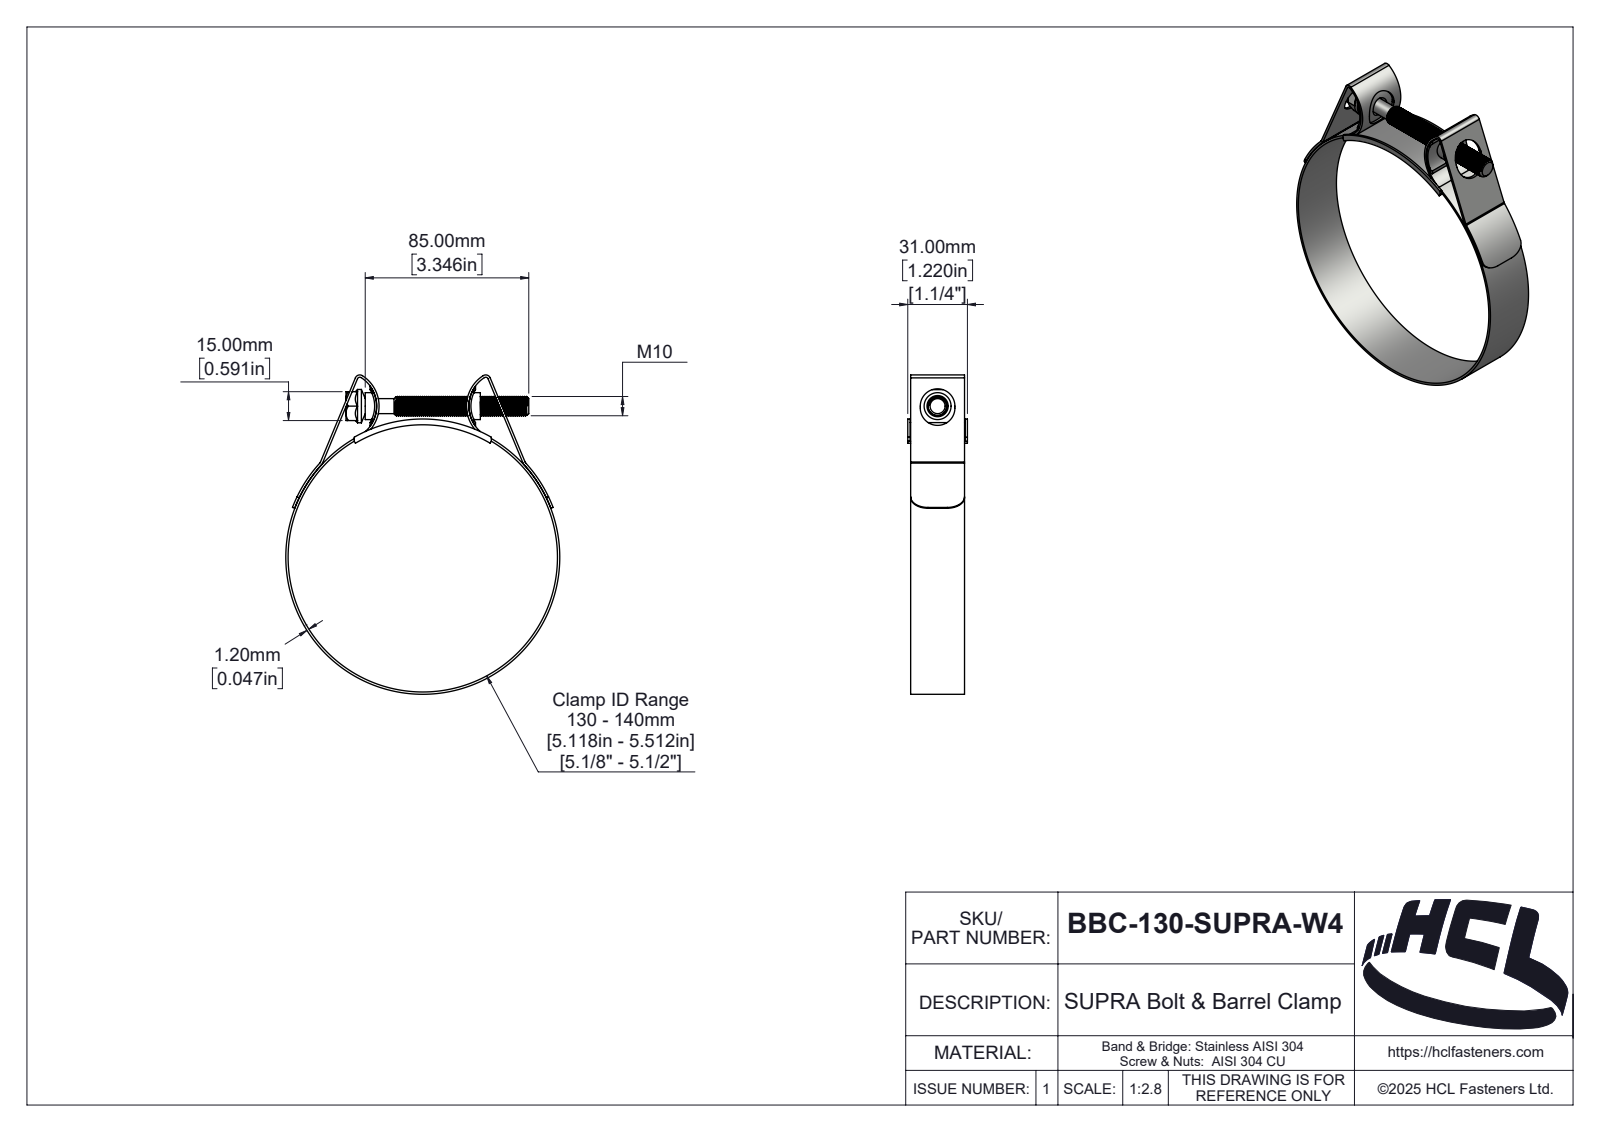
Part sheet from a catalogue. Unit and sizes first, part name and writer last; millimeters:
Units: millimetres
Overall size (bounding box): 165.9 × 142.4 × 31
Round holes (diameter × count): ⌀140 ×1
Round bosses / shafts (diameter × count): ⌀142.4 ×1, ⌀17.32 ×1, ⌀14 ×1, ⌀10 ×1, ⌀7.8 ×1
Partial cylindrical surfaces — rounded edges, fillets, slot ends (radius × count): R1 ×4, R1.3 ×2, R2 ×2, R2.5 ×2, R3.2 ×2, R9 ×2, R16.49 ×2, R17.49 ×2
Main face-to-face distances: 1.2, 28, 1.5, 29.5, 29.8, 28.3, 31, 28.6, 15, 2.5
Volume: 31 247 mm³ · Surface area: 46 325 mm²
Bodies: 5 solids, 382 faces (46 planar, 249 cylindrical, 87 other)
Part name (STEP PRODUCT): BBC-130-SUPRA-W4
STEP written by: SolidWorks 2025 (AUTOMOTIVE_DESIGN)
